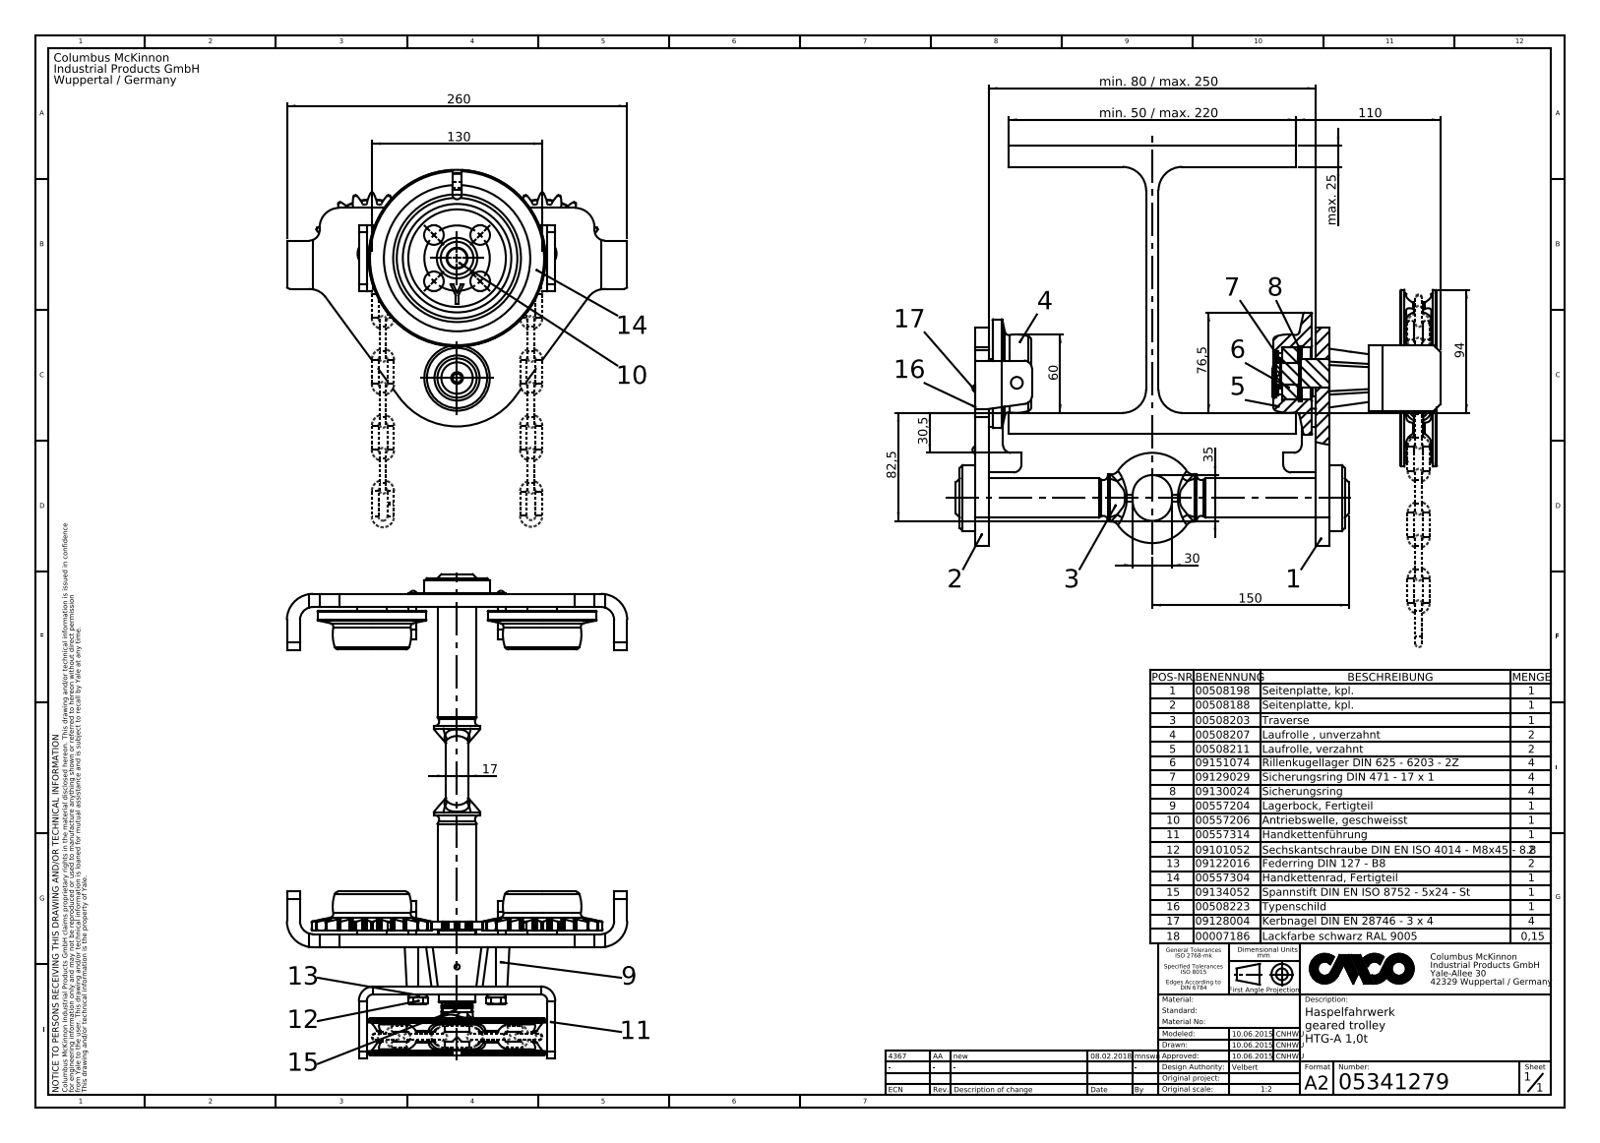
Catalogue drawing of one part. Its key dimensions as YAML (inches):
part_name: "HTG-A 1,0t"
step_written_by: "SolidWorks 2015 (AUTOMOTIVE_DESIGN)"
units: inches
bodies: {solids: 68, faces: 2023, planar: 446, cylindrical: 932, other: 645}
overall_size: [19.685, 15.082, 14.567]
volume: 371.8
surface_area: 1724
round_holes:
  - {diameter: 0.067, count: 8}
  - {diameter: 0.098, count: 8}
  - {diameter: 0.118, count: 5}
  - {diameter: 0.138, count: 4}
  - {diameter: 0.354, count: 4}
  - {diameter: 0.591, count: 4}
  - {diameter: 0.268, count: 3}
  - {diameter: 0.079, count: 2}
  - {diameter: 0.319, count: 2}
  - {diameter: 0.638, count: 2}
  - {diameter: 0.866, count: 2}
  - {diameter: 1.122, count: 2}
round_bosses_or_shafts:
  - {diameter: 0.197, count: 22}
  - {diameter: 0.205, count: 4}
  - {diameter: 3.268, count: 2}
  - {diameter: 1.673, count: 2}
  - {diameter: 0.937, count: 2}
  - {diameter: 0.669, count: 2}
  - {diameter: 0.63, count: 2}
  - {diameter: 0.555, count: 2}
partial_cylinders:
  - {radius: 0.039, count: 110}
  - {radius: 0.787, count: 92}
  - {radius: 0.059, count: 56}
  - {radius: 0.394, count: 26}
  - {radius: 0.067, count: 8}
  - {radius: 0.098, count: 8}
  - {radius: 0.236, count: 8}
  - {radius: 0.591, count: 4}
face_to_face_distances: [0.63, 8.031, 8.661, 7.402, 0.374, 5.128, 5.502, 0.394, 10.236, 4.734]
hole_center_spacings: [0.393, 0.722, 5.118, 2.002, 0.167, 0.33, 0.556, 0.848]
